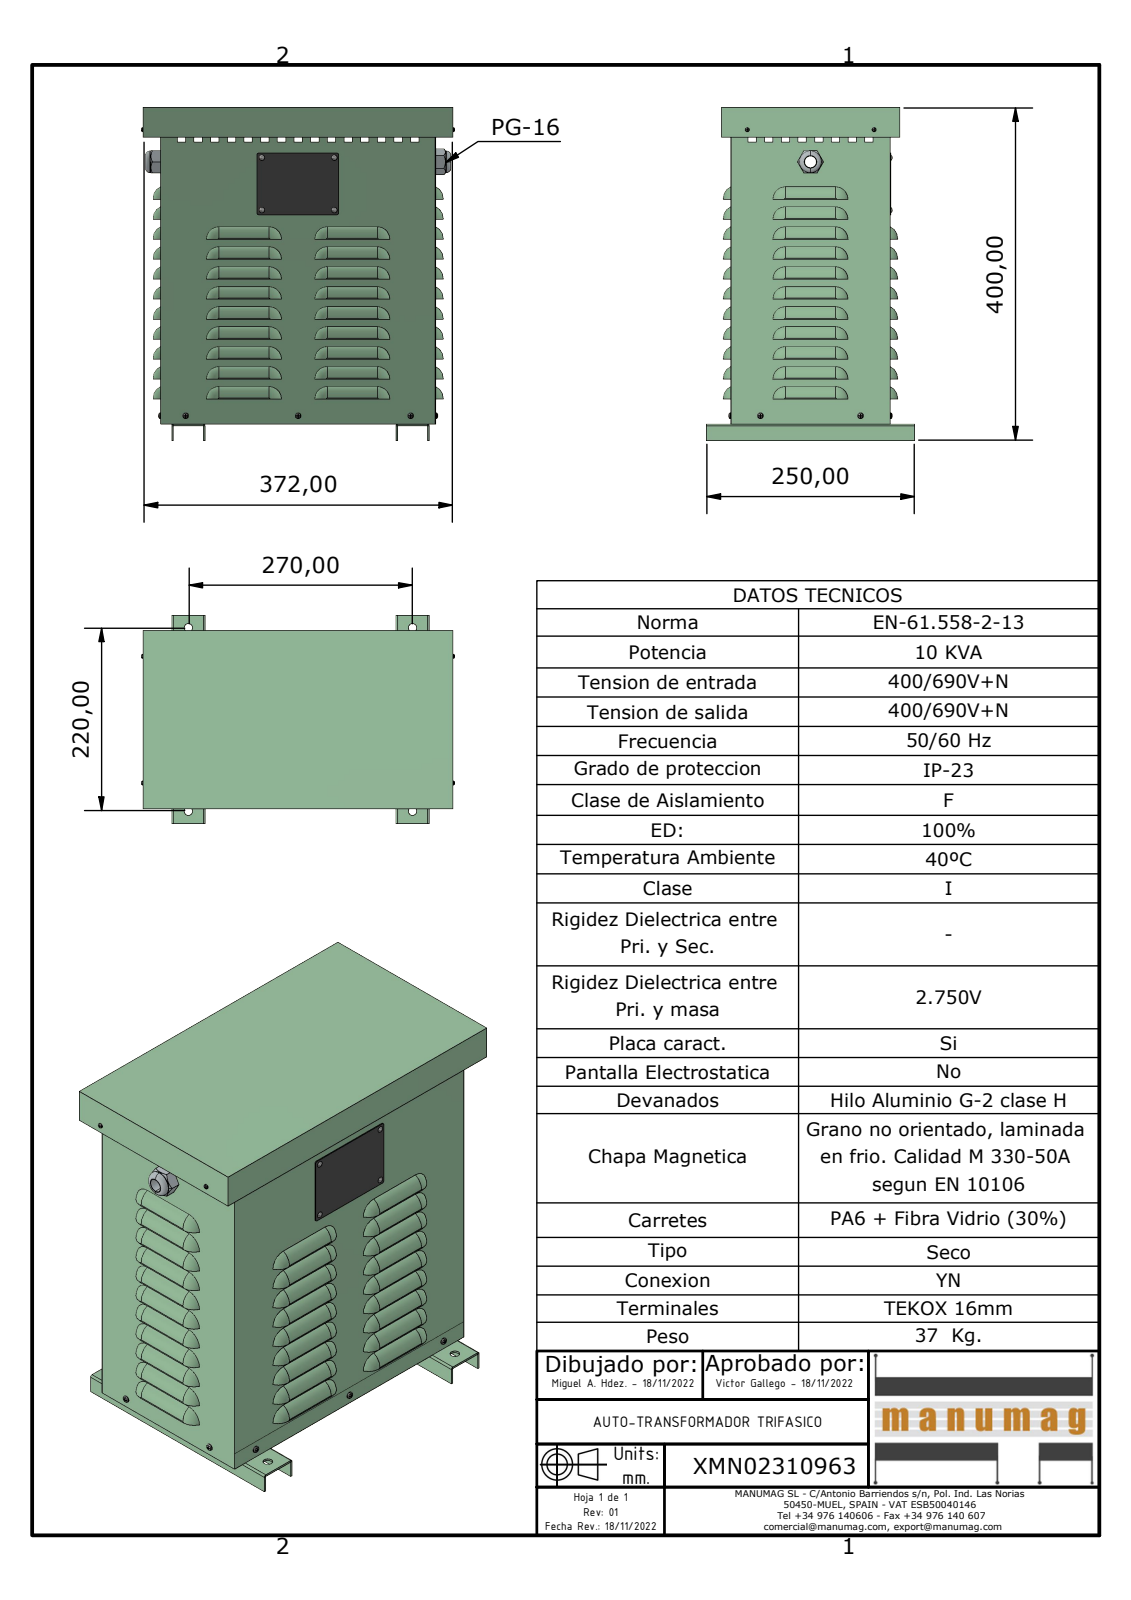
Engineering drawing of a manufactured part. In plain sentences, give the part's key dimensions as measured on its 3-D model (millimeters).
The part is named "XMN02310963; JE010 NACIONAL CUERPO; JE010 NACIONAL BASE; PLACA CARACTERISTICAS (+6 more)". Its 3-D file was written by "Autodesk Inventor 2023 (AUTOMOTIVE_DESIGN)". It is 26 solids with 1888 faces: 958 planar, 396 cylindrical and 534 other. Overall it measures 400.63 by 376.16 by 250 millimeters. Its volume is 883 061 cubic millimeters and its surface area 1 346 000 square millimeters. Round holes: 9 of diameter 4, 4 of diameter 3, 4 of diameter 10, 1 of diameter 14, 1 of diameter 24. Round bosses or shafts: 5 of diameter 3.5, 5 of diameter 3.18, 4 of diameter 3.2, 2 of diameter 2.5, 2 of diameter 2.26, 1 of diameter 26, 1 of diameter 23, 1 of diameter 22.5. Partial cylindrical surfaces (rounded edges, fillets, slot ends): 66 of radius 14, 42 of radius 7, 42 of radius 15, 12 of radius 1.5, 8 of radius 5, 8 of radius 5.5, 5 of radius 0.5, 4 of radius 0.5. The main face-to-face distances are 0.5, 190.5, 1.5, 190, 379.12, 329.5, 191, 380.62, 329, 330. The hole center spacings are 63, 85.25, 87, 107.42, 135, 152, 220, 250.8.
